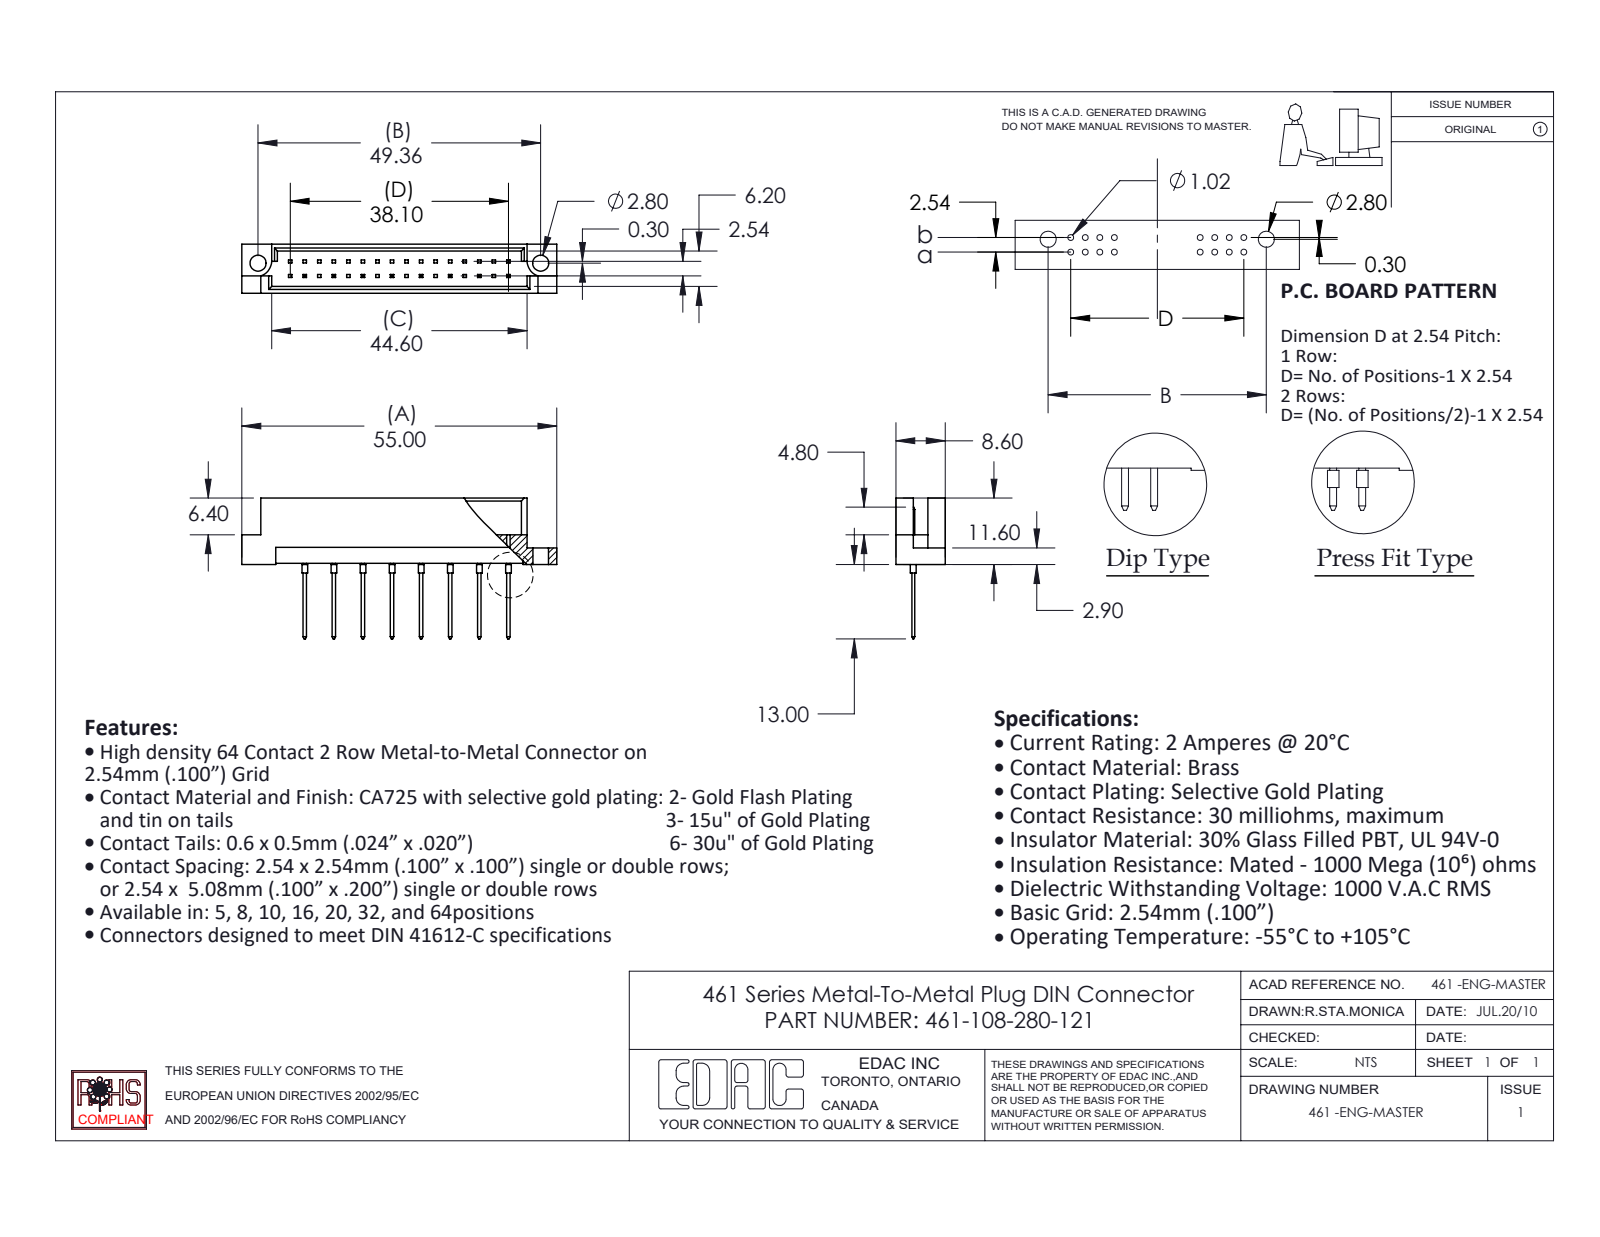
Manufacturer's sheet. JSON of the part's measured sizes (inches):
{"part_name": "461-108-280-121; 461-290_80; 461 Part_32", "step_written_by": "SolidWorks 2020 (CONFIG_CONTROL_DESIGN)", "units": "inches", "bodies": {"solids": 9, "faces": 352, "planar": 330, "cylindrical": 22, "other": 0}, "overall_size": [2.165, 0.969, 0.339], "volume_in3": 0.166, "surface_area_in2": 5.687, "round_holes": [[0.11, 2]], "round_bosses_or_shafts": [[0.039, 8]], "partial_cylinders_radius": [[0.11, 2]], "face_to_face_distances": [0.047, 0.291, 0.339, 0.244, 0.197, 0.109, 0.229, 0.062, 0.182, 0.129], "hole_center_spacings": [1.943]}
